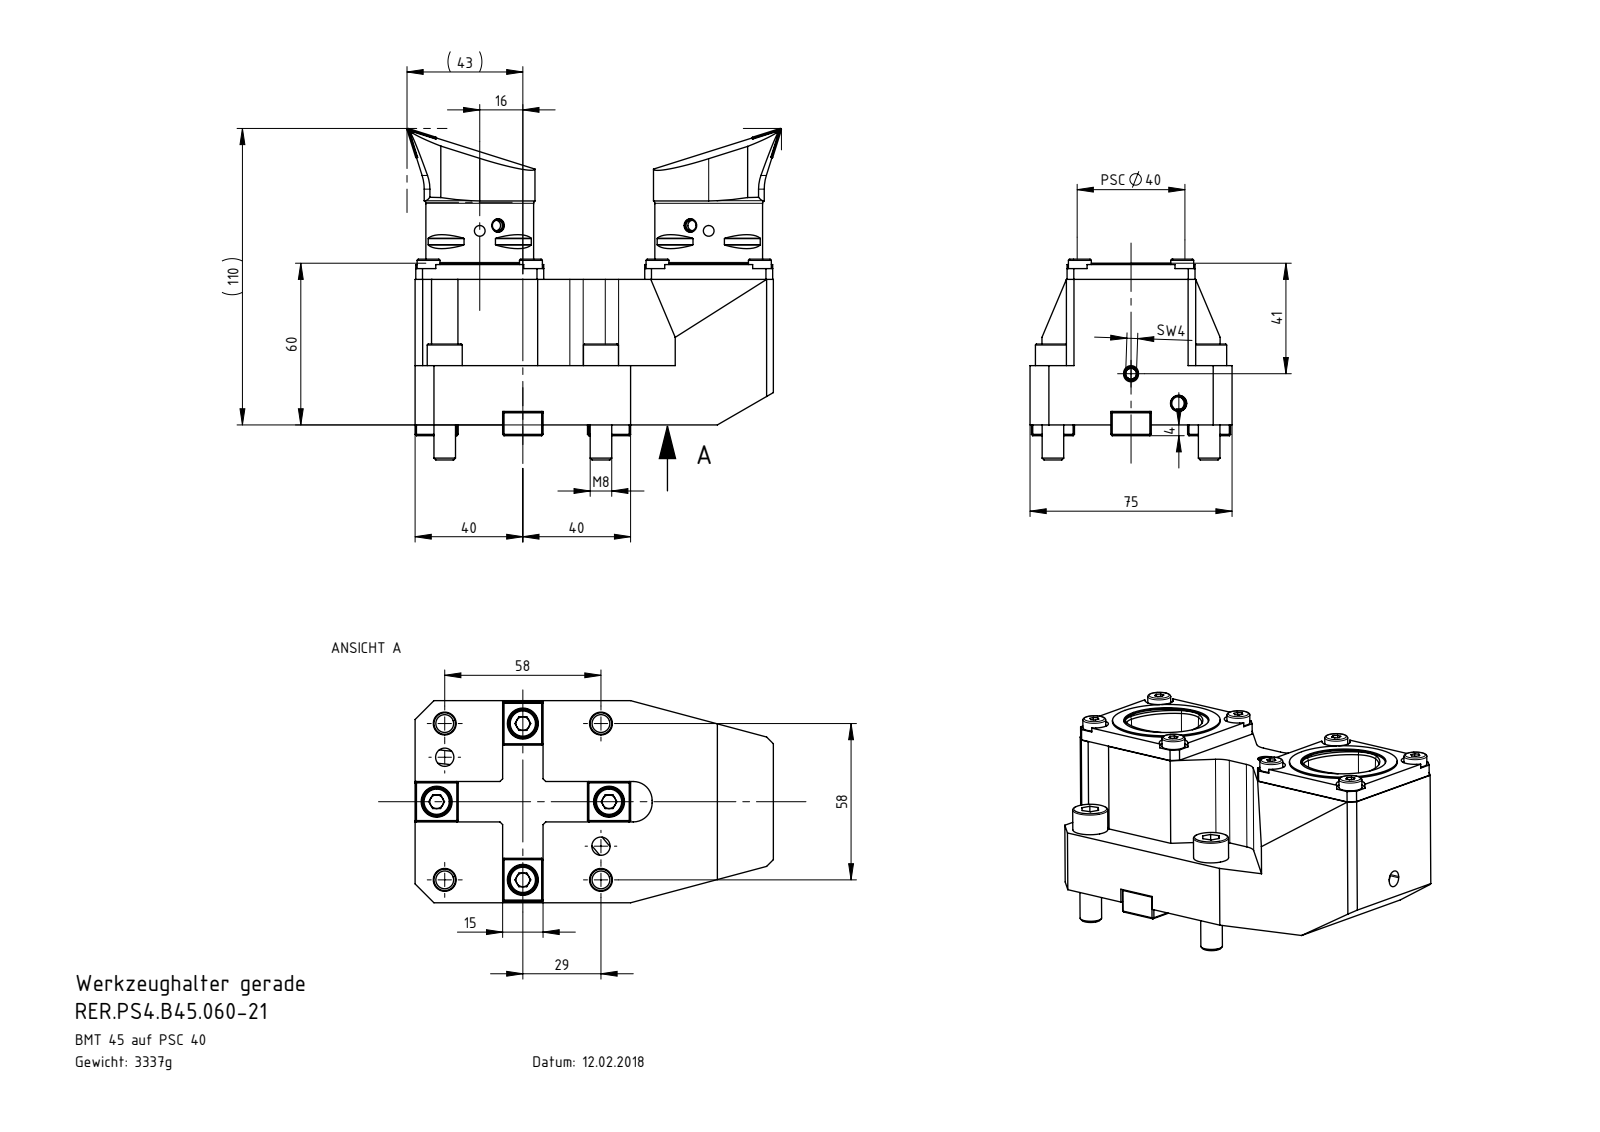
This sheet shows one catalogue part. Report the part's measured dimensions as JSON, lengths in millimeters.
{"part_name": "KVT_MB_600_060; RER-PS4.B45.060-21_A; DIN 3771 - 38x1.5; U40-PS4.048.006 (+8 more)", "step_written_by": "SolidWorks 2022 (AUTOMOTIVE_DESIGN)", "units": "millimeters", "bodies": {"solids": 51, "faces": 1728, "planar": 735, "cylindrical": 388, "other": 605}, "overall_size": [133, 75, 74.5], "volume_mm3": 349122, "surface_area_mm2": 119958, "round_holes": [[5, 12], [4.2, 8], [5.5, 8], [2.5, 6], [6, 5], [3, 4], [3.3, 4], [6.5, 4], [8.5, 4], [11, 4], [6.8, 2], [23, 2]], "round_bosses_or_shafts": [[8.5, 8], [5, 8], [6, 7], [8, 5], [13, 4], [10, 4], [5.5, 4], [3, 4]], "partial_cylinders_radius": [[3.5, 8], [5.25, 8], [7, 8], [3, 4], [0.2, 2], [2.75, 2], [12, 2], [9, 1]], "face_to_face_distances": [22, 54, 13.5, 5, 7, 47.5, 15, 32, 49, 16.5], "hole_center_spacings": [85, 20.25, 26.87, 36.36, 38, 58, 12, 12.69]}
